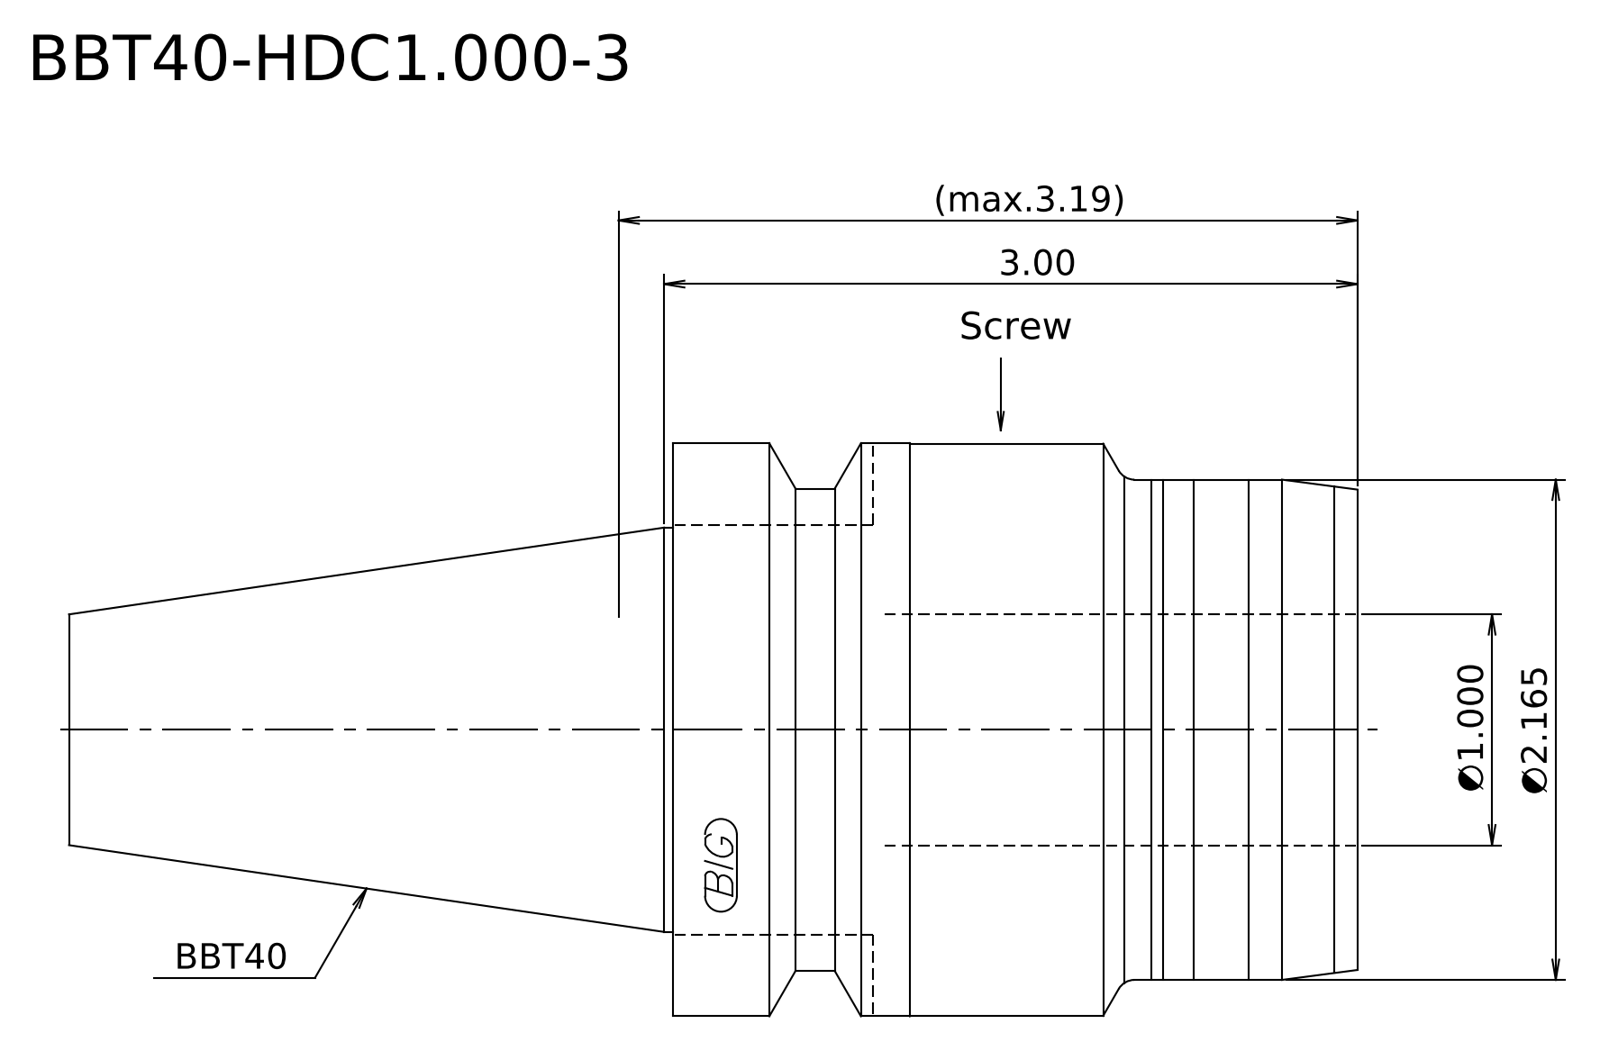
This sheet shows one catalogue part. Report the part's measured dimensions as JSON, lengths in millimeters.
{"step_written_by": "Kubotek KeyCreator 2011 V10.0.2 (22737) (automotive_design)", "units": "millimeters", "bodies": {"solids": 1, "faces": 15, "planar": 3, "cylindrical": 6, "other": 6}, "overall_size": [141.6, 63, 63], "volume_mm3": 273045, "surface_area_mm2": 27016, "round_bosses_or_shafts": [[63, 1], [62.9, 1], [55, 1], [53, 1], [44.45, 1]], "face_to_face_distances": [75.2, 141.6, 66.4]}
